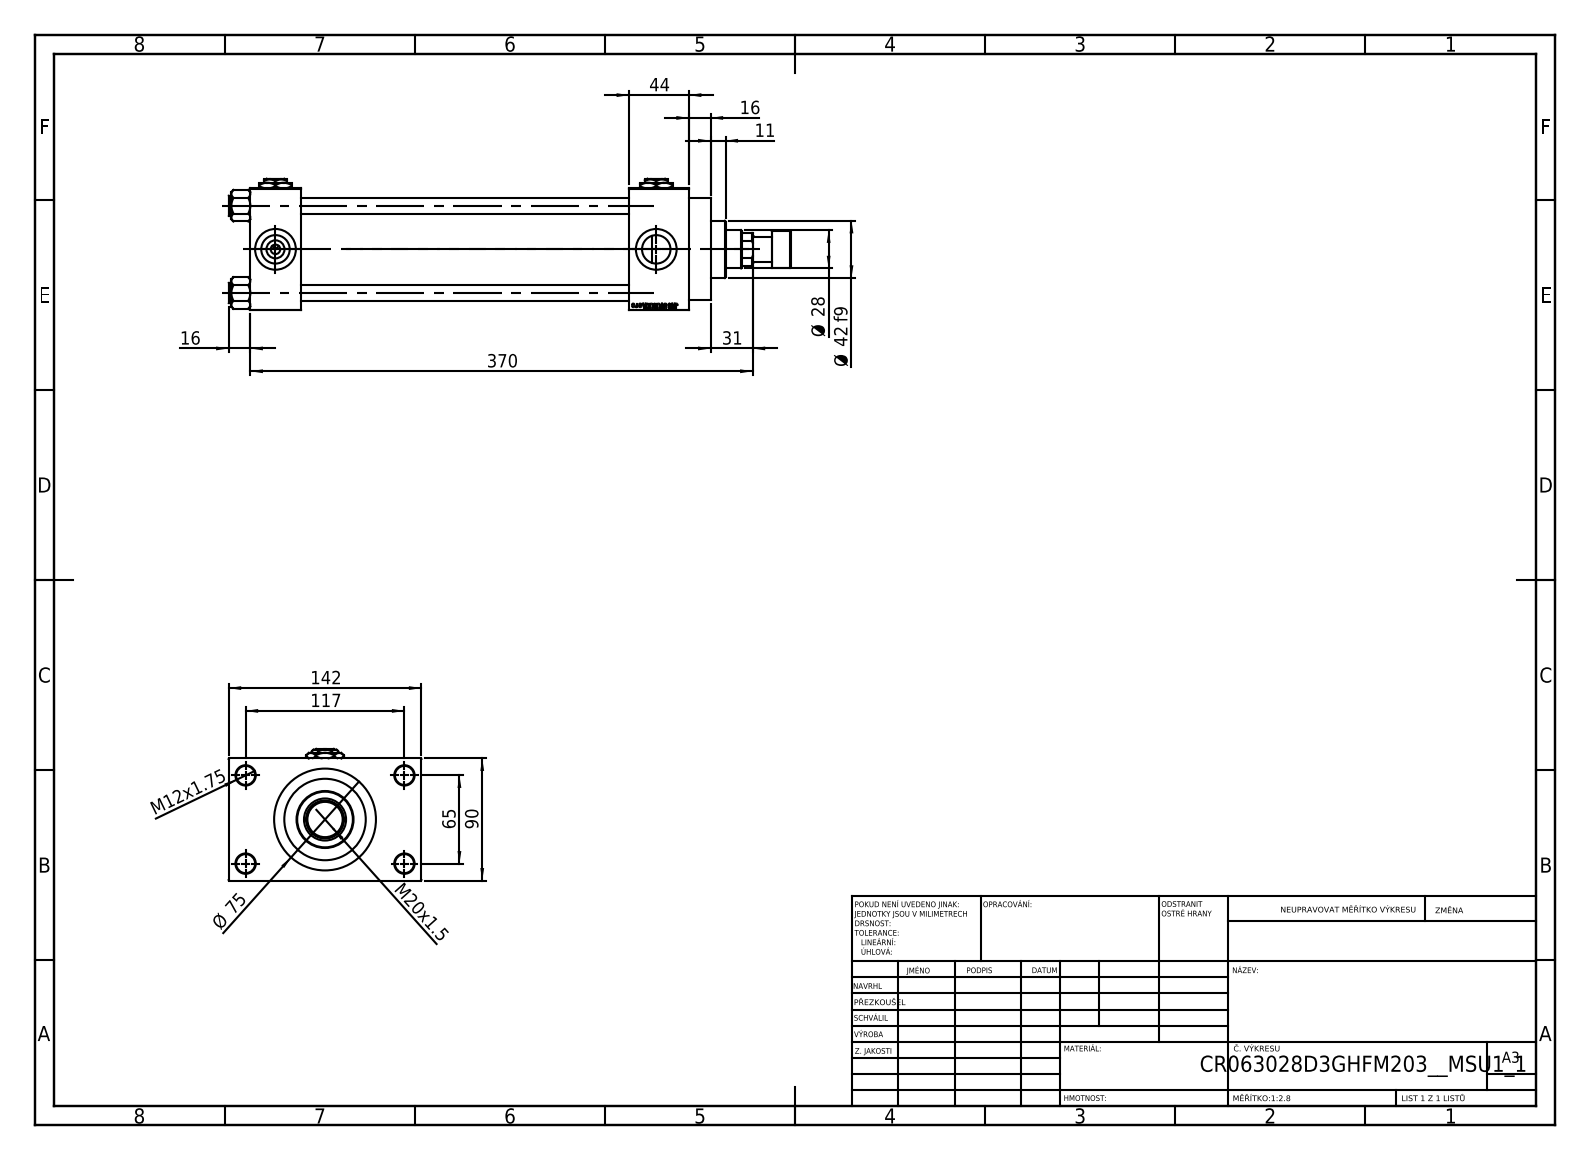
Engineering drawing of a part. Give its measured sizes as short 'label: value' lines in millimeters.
name: V215CR_D_Body; V215CR_D_TYCINKA; V215CR_VCP_D; NUT_M5_D (+3 more)
written by: SolidWorks 2019 (CONFIG_CONTROL_DESIGN)
unit: mm
bodies: 14 solids, 1218 faces (549 planar, 103 cylindrical, 566 other)
size: 414 × 142 × 97
volume: 1 412 000 mm³; area: 327 780 mm²
holes: 4× ⌀12, 4× ⌀14, 4× ⌀20.96, 4× ⌀30, 3× ⌀7, 1× ⌀18.5, 1× ⌀28, 1× ⌀31, 1× ⌀50, 1× ⌀60, 1× ⌀63
bosses: 4× ⌀15, 1× ⌀75, 1× ⌀69, 1× ⌀42, 1× ⌀27, 1× ⌀18
face distances: 90, 242, 37, 279, 286, 323, 44, 26, 116, 16
hole spacings: 26.35, 45.47, 64.3, 66.92, 69.81, 90.65, 111.34, 65
